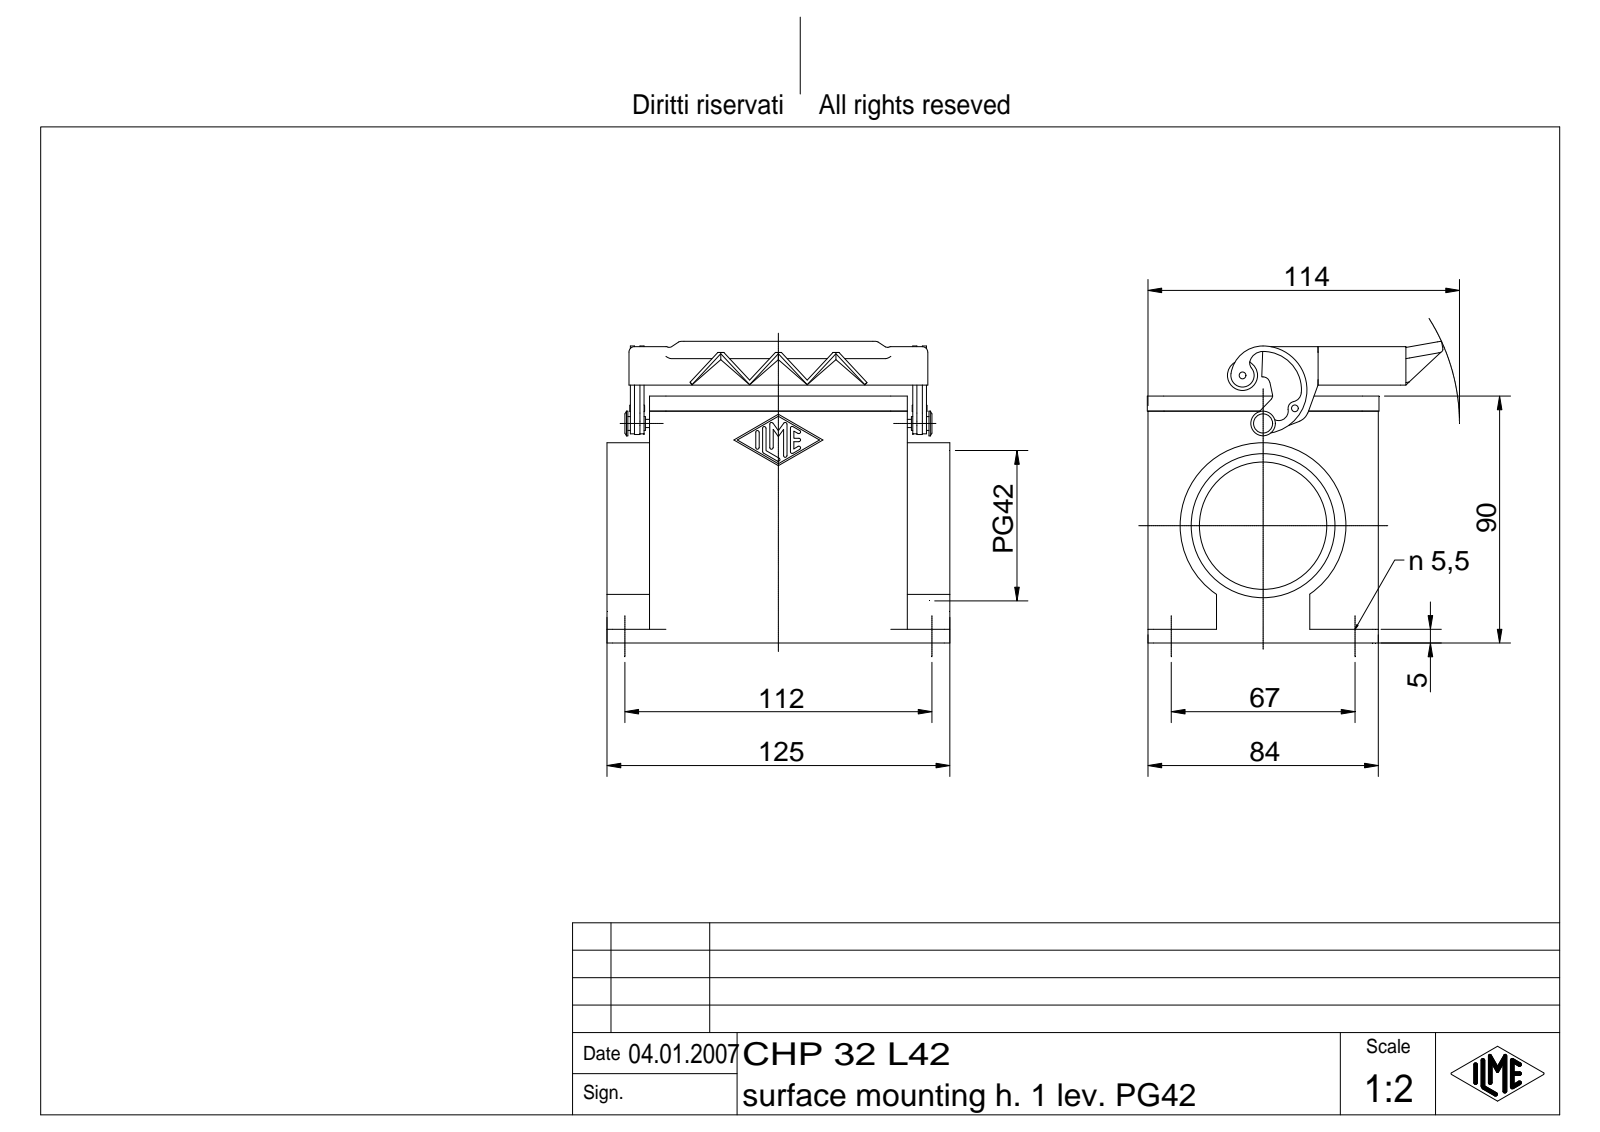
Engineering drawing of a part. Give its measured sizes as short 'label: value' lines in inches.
name: CHP 32 L42
written by: Autodesk Inventor 7 (AUTOMOTIVE_DESIGN)
unit: in
bodies: 4 solids, 491 faces (166 planar, 145 cylindrical, 180 other)
size: 4.921 × 4.33 × 4.246
volume: 14.45 in³; area: 165.4 in²
holes: 4× ⌀0.217, 1× ⌀0.079, 1× ⌀1.83, 1× ⌀2.066
bosses: 1× ⌀2.382, 1× ⌀0.433, 1× ⌀0.354, 1× ⌀0.197, 1× ⌀0.118, 1× ⌀0.098
rounds: 16× R0.079, 14× R0.024, 9× R0.059, 8× R0.236, 4× R0.006, 4× R0.118, 3× R0.039, 3× R0.098
face distances: 0.118, 3.189, 3.307, 0.157, 3.071, 0.453, 3.248, 3.327, 2.795, 3.169
hole spacings: 2.638, 4.409, 5.138, 1.744
